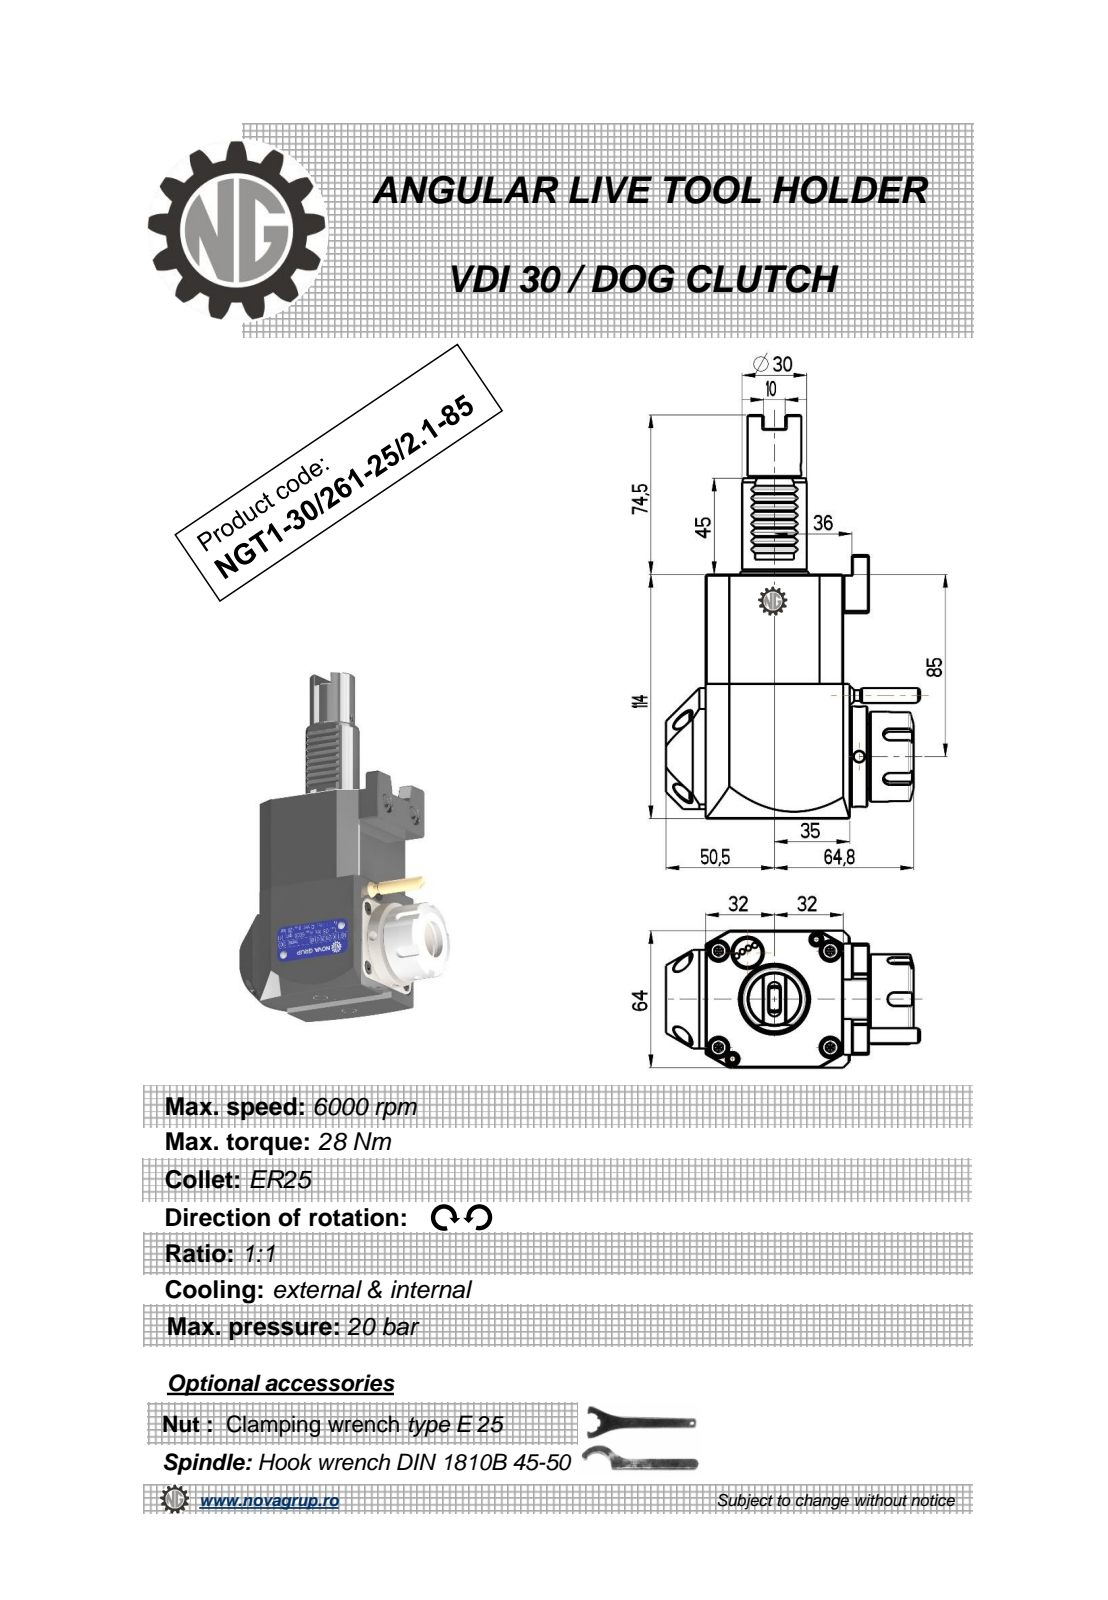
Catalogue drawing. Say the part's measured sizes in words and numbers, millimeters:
The part is named "NGT1_30_261_25_2_1_85". Its 3-D file was written by "PRO/ENGINEER BY PARAMETRIC TECHNOLOGY CORPORATION, 2010280 (CONFIG_CONTROL_DESIGN)". It is 1 solid with 390 faces: 194 planar, 64 cylindrical and 132 other. Overall it measures 188.5 by 118.33 by 64 millimeters. Its volume is 596 497 cubic millimeters and its surface area 56 824 square millimeters. Round holes: 2 of diameter 5, 1 of diameter 2.5, 1 of diameter 3, 1 of diameter 4.2, 1 of diameter 20.3. Round bosses or shafts: 1 of diameter 47, 1 of diameter 42, 1 of diameter 35, 1 of diameter 30, 1 of diameter 25, 1 of diameter 8.96, 1 of diameter 7, 1 of diameter 5. Partial cylindrical surfaces (rounded edges, fillets, slot ends): 8 of radius 0.3, 6 of radius 0.26, 5 of radius 3, 2 of radius 0.5, 2 of radius 1, 2 of radius 6, 2 of radius 160, 1 of radius 32. The main face-to-face distances are 64, 114, 9, 3, 0.5, 67.2, 3.2, 67, 0.8, 8.8. The hole center spacings are 33.19, 107.85, 135.
